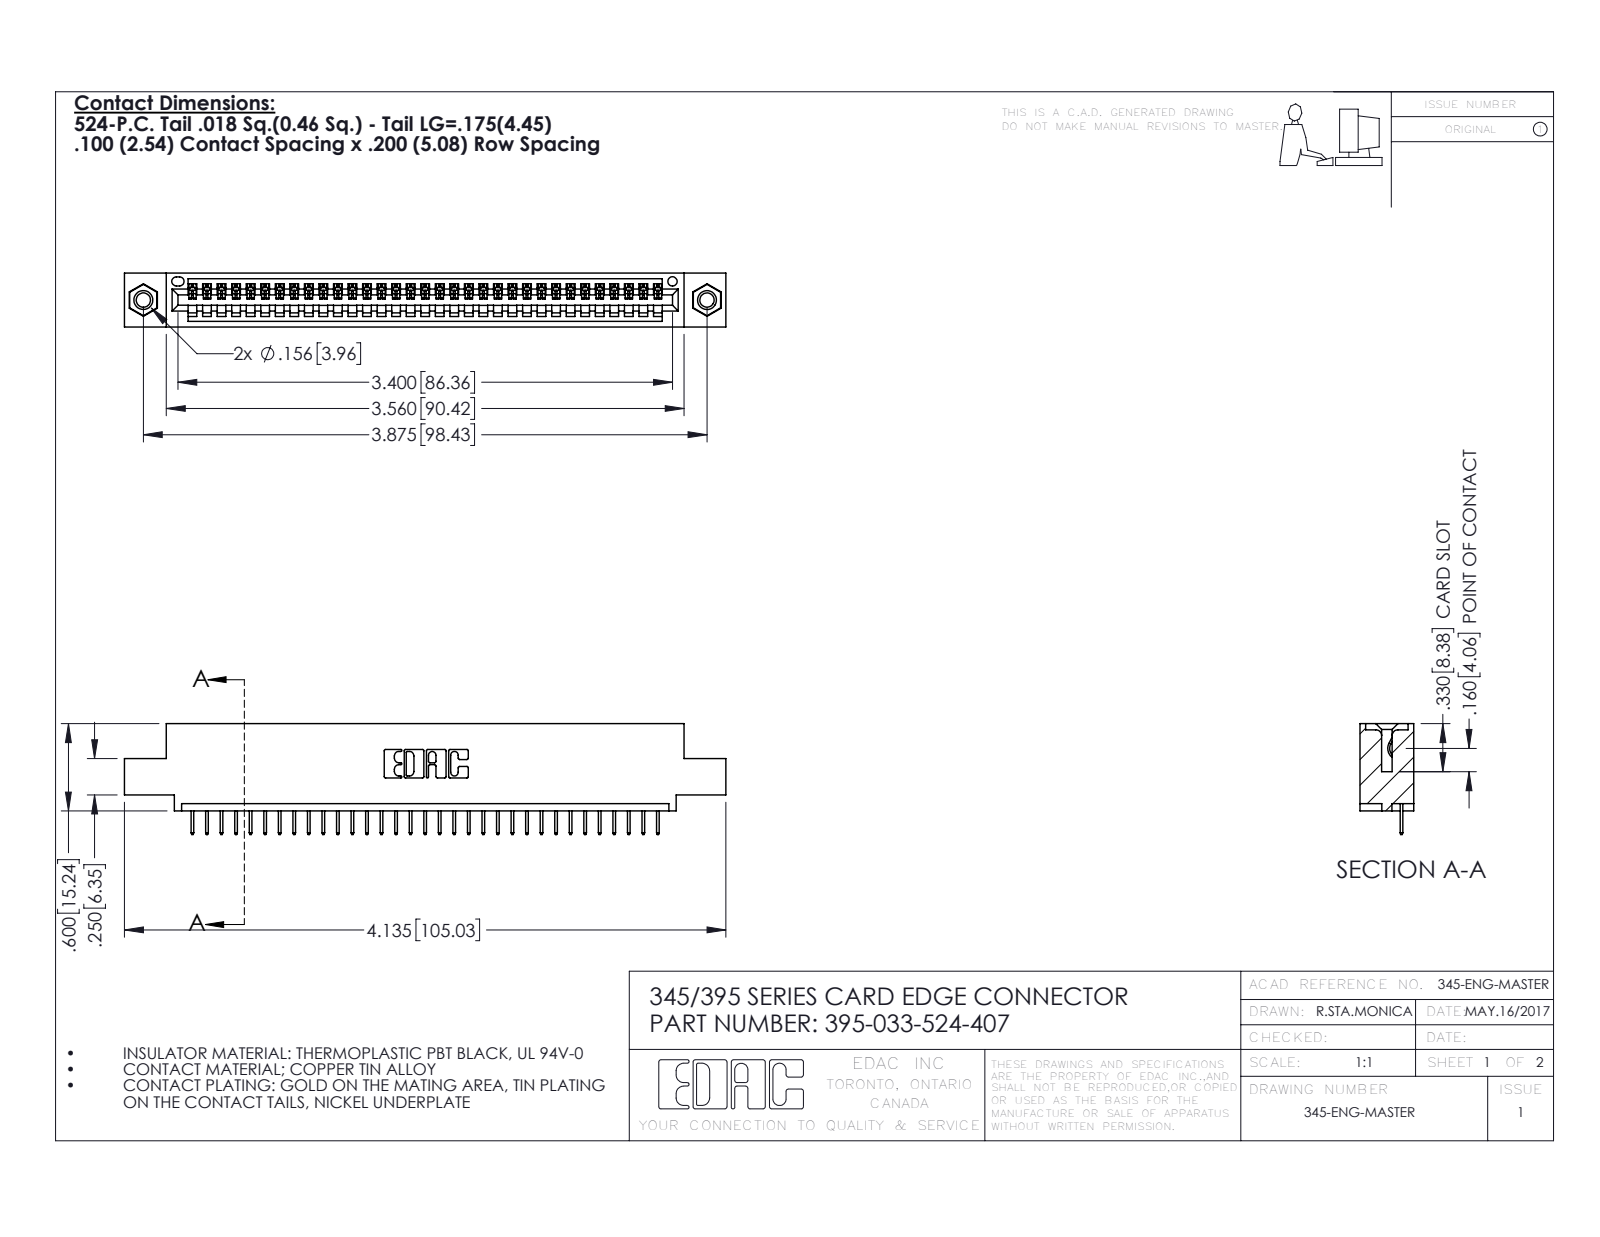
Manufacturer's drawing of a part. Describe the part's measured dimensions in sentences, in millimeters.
The part is named "345-250-001_345-250-005-103; 395-033-524-407; 345-292-001_345-293-124; 345 Part_0.110 Offset - 0.156 Dia-TI". Its 3-D file was written by "SolidWorks 2016 (CONFIG_CONTROL_DESIGN)". It is 36 solids with 2236 faces: 1634 planar, 586 cylindrical and 16 other. Overall it measures 105 by 19.4 by 9.4 millimeters. Its volume is 9 680 cubic millimeters and its surface area 12 450 square millimeters. Round holes: 2 of diameter 2.5, 2 of diameter 3.2, 2 of diameter 4, 1 of diameter 1.6. Round bosses or shafts: 2 of diameter 3.9. Partial cylindrical surfaces (rounded edges, fillets, slot ends): 66 of radius 0.2, 22 of radius 0.3, 6 of radius 0.2, 6 of radius 0.8, 3 of radius 0.7, 2 of radius 0.8, 2 of radius 1, 1 of radius 0.4. The main face-to-face distances are 1.8, 7.6, 9.4, 5.1, 2.5, 6.9, 0.6, 5.7, 1.8, 3.8. The hole center spacings are 6.9, 92.5, 98.4.
